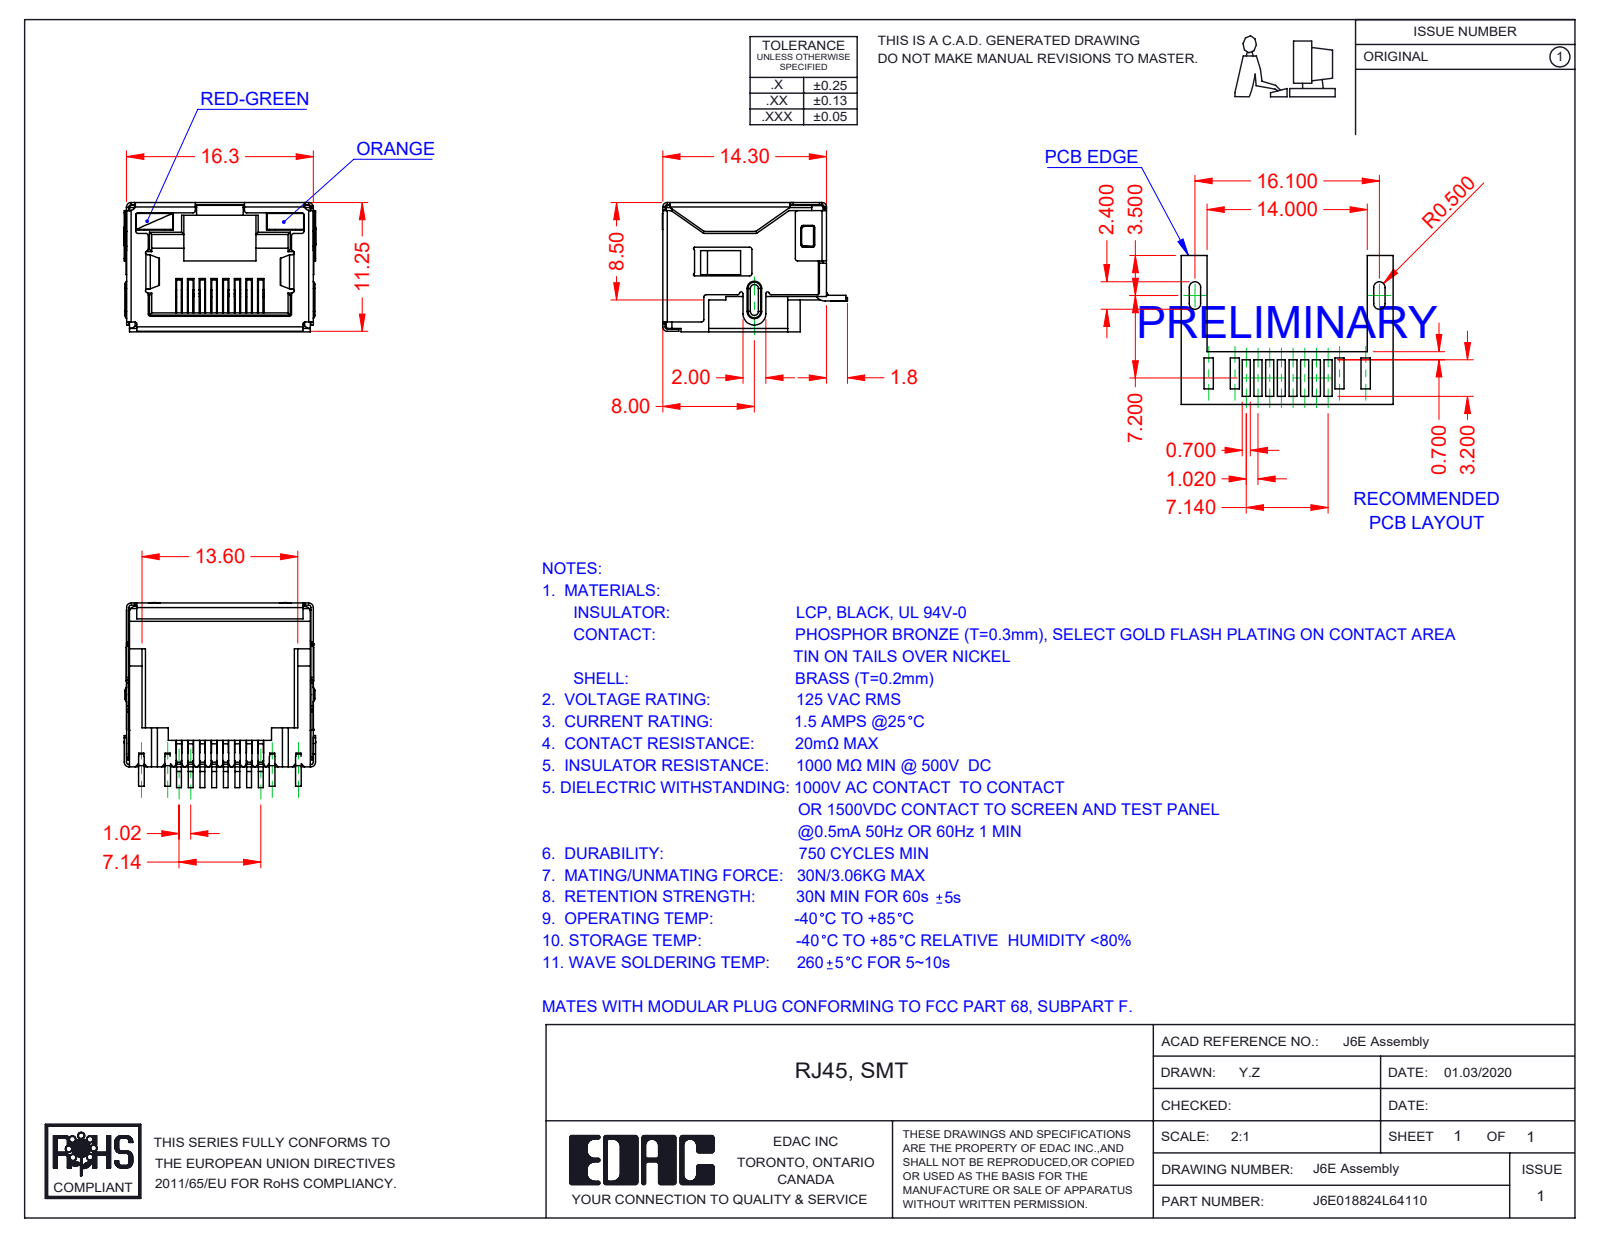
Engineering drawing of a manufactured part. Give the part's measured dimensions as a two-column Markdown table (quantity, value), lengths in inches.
| quantity | value |
| --- | --- |
| part name | 6E LED LH_6-Red-Green; 6E Shield_LED; 6E LED RH_4-Orange; 6E Insulator_LED (+2 more) |
| STEP written by | SolidWorks 2016 (CONFIG_CONTROL_DESIGN) |
| units | inches |
| bodies | 12 solids, 1498 faces (1099 planar, 349 cylindrical, 50 other) |
| overall size | 0.659 × 0.636 × 0.445 |
| volume | 0.068 in³ |
| surface area | 6.27 in² |
| partial cylindrical surfaces (radius × count) | 0.008 × 82, 0.01 × 17, 0.016 × 13, 0.02 × 13, 0.004 × 10, 0.006 × 7, 0.012 × 4, 0.039 × 3 |
| main face-to-face distances | 0.435, 0.632, 0.634, 0.624, 0.437, 0.445, 0.094, 0.028, 0.388, 0.019 |
